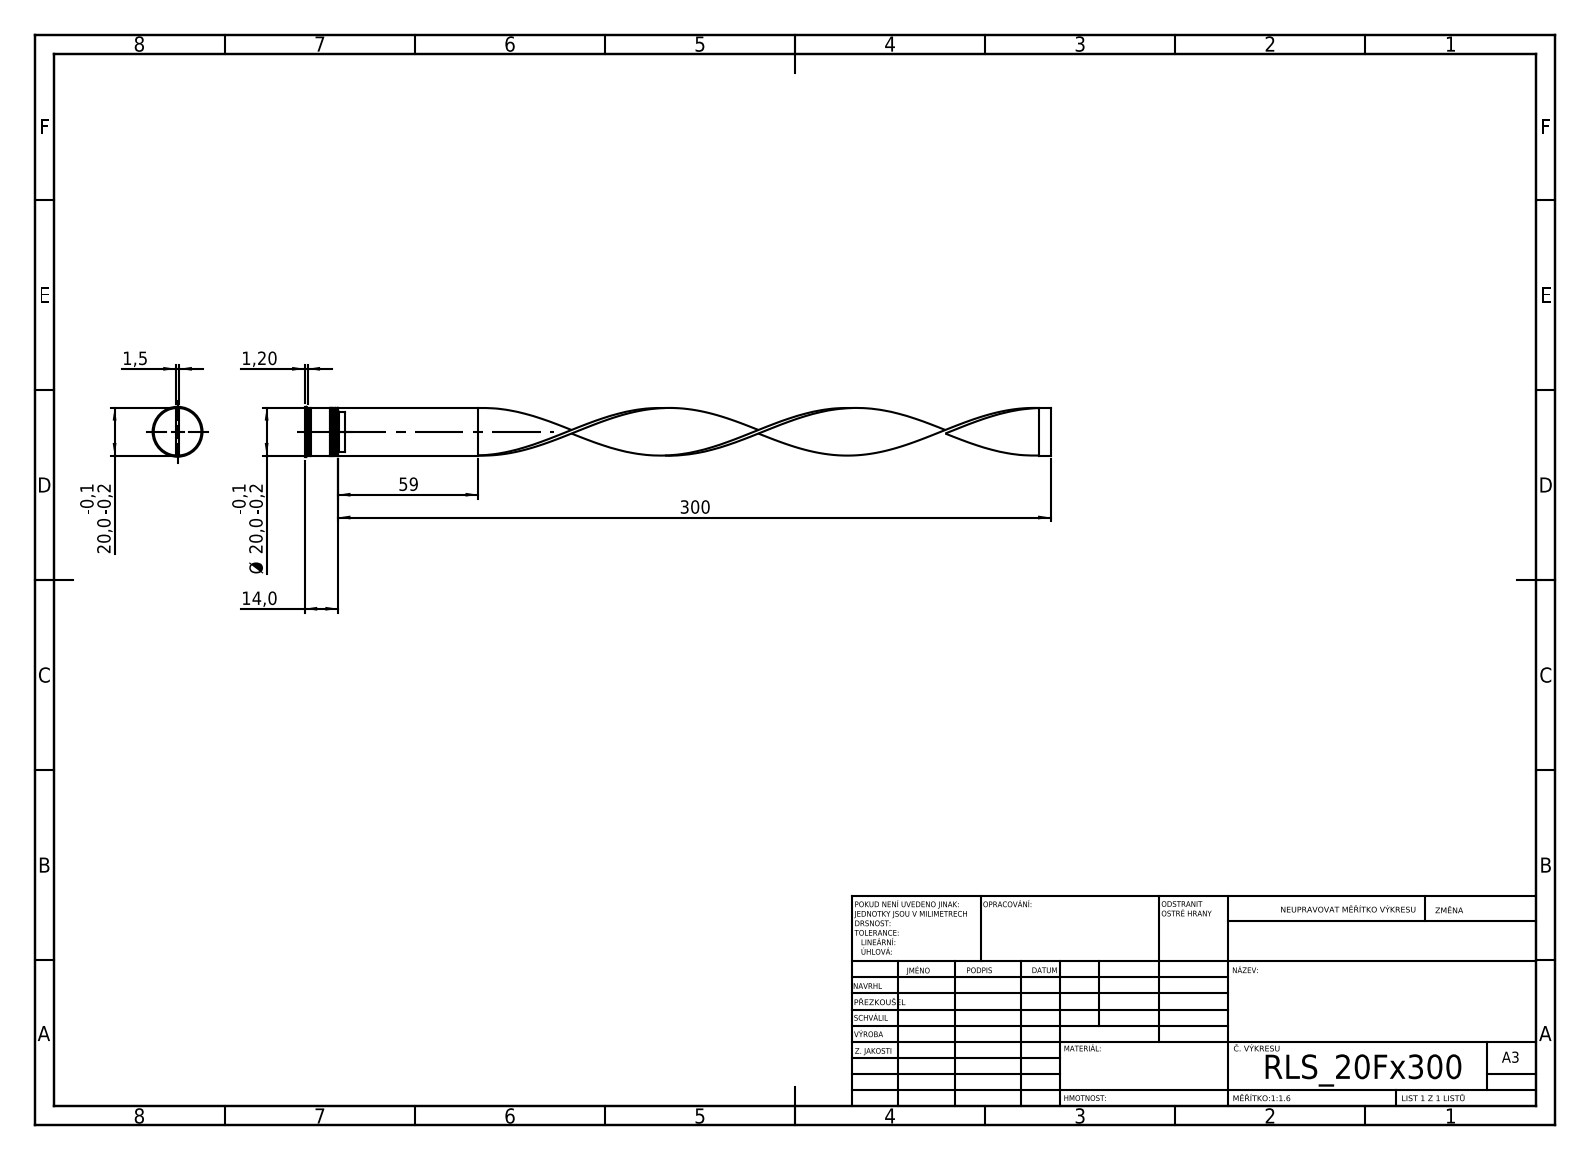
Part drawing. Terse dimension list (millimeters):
written by: SolidWorks 2019 (CONFIG_CONTROL_DESIGN)
unit: mm
bodies: 3 solids, 98 faces (43 planar, 28 cylindrical, 27 other)
size: 314 × 21 × 21
volume: 14 150 mm³; area: 16 247 mm²
bosses: 1× ⌀21, 1× ⌀20, 1× ⌀19.4, 1× ⌀16.8
rounds: 1× R8.5
face distances: 1.5, 0.7, 2.2, 0.8, 11.7, 11, 10.2, 9.5, 16, 4.3
